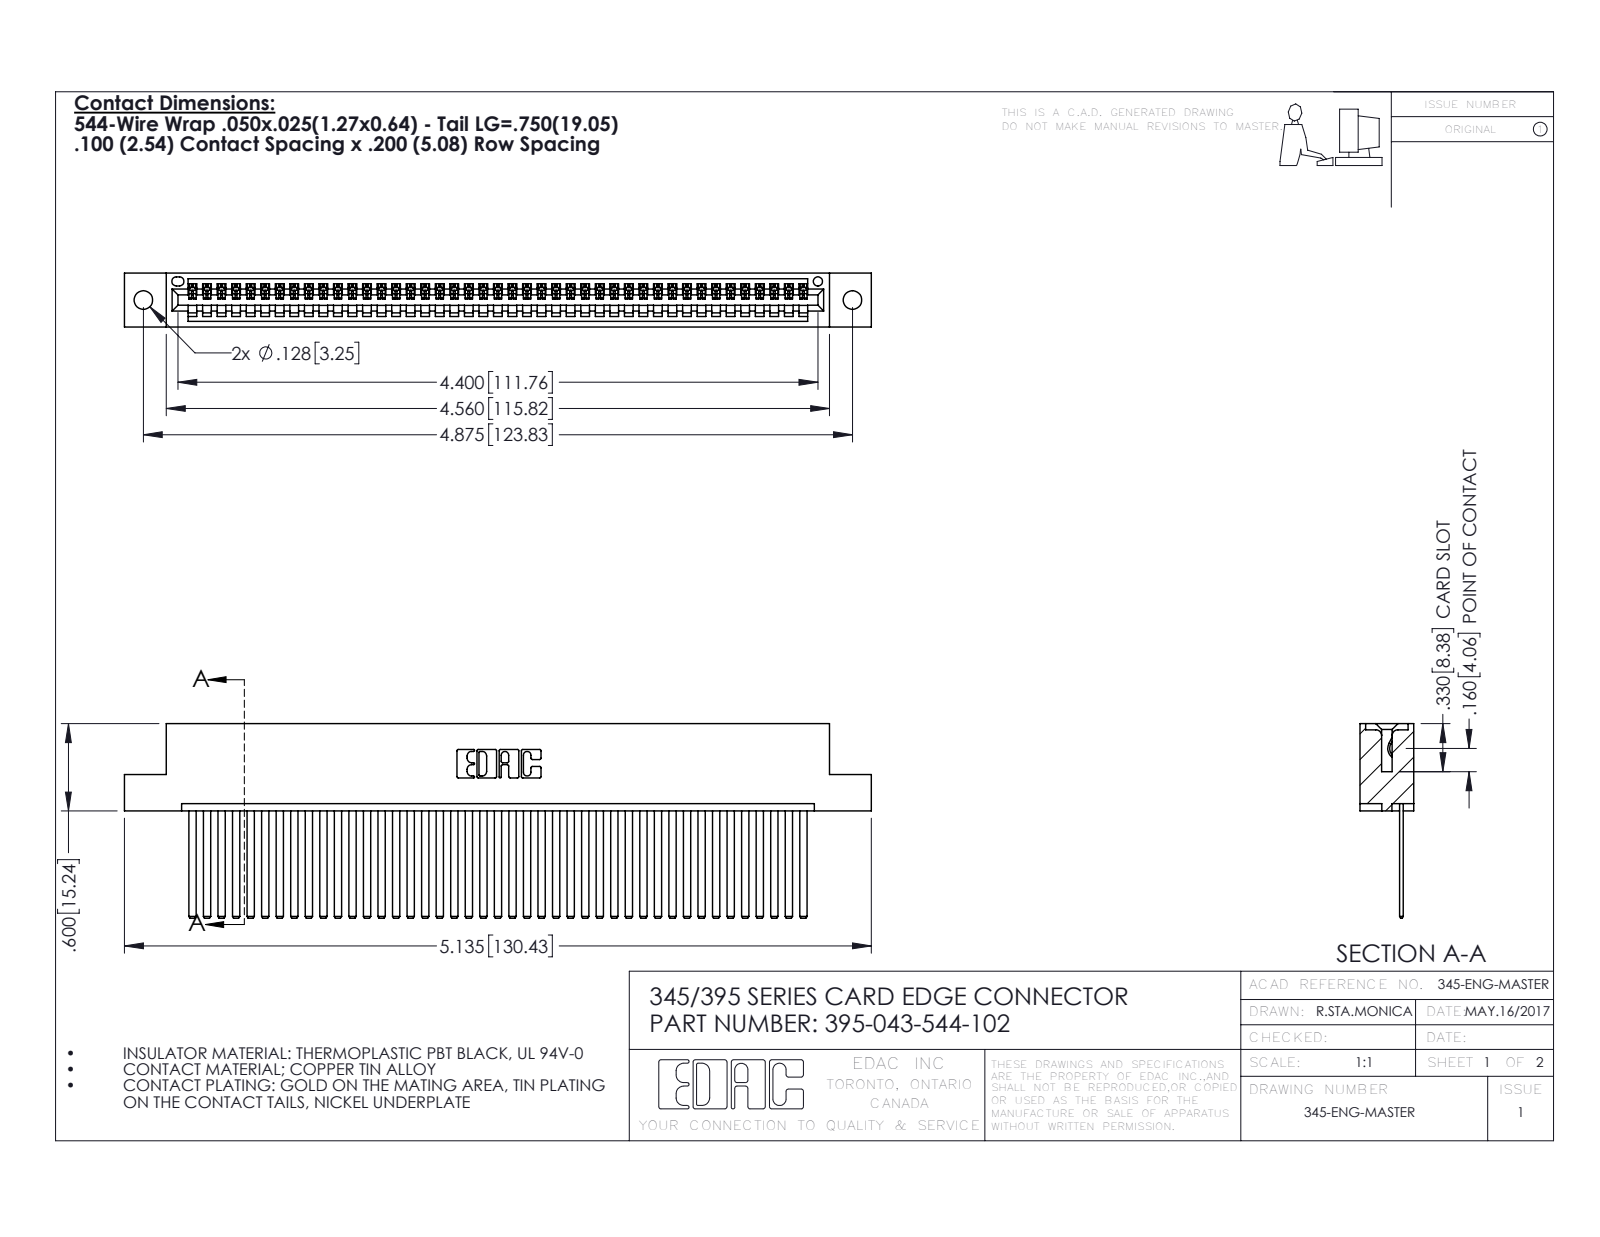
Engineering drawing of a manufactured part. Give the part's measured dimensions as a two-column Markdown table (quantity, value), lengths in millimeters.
| quantity | value |
| --- | --- |
| part name | 345 Part_Flush Mounting Lugs - 0.128 Dia; 395-043-544-102; 345-292-001_345-293-144 |
| STEP written by | SolidWorks 2016 (CONFIG_CONTROL_DESIGN) |
| units | millimeters |
| bodies | 44 solids, 2362 faces (1628 planar, 734 cylindrical, 0 other) |
| overall size | 130.4 × 34 × 9.4 |
| volume | 12 900 mm³ |
| surface area | 18 320 mm² |
| round holes (diameter × count) | 3.3 × 2, 1.6 × 1 |
| partial cylindrical surfaces (radius × count) | 0.2 × 86, 0.3 × 22, 0.2 × 6, 0.8 × 6, 0.7 × 3, 0.8 × 2, 1 × 2, 0.4 × 1 |
| main face-to-face distances | 1.8, 7.6, 0.6, 2.5, 6.9, 9.4, 5.1, 5.7, 3.8, 1.8 |
| hole center spacings | 6.9, 117.8, 123.8 |
